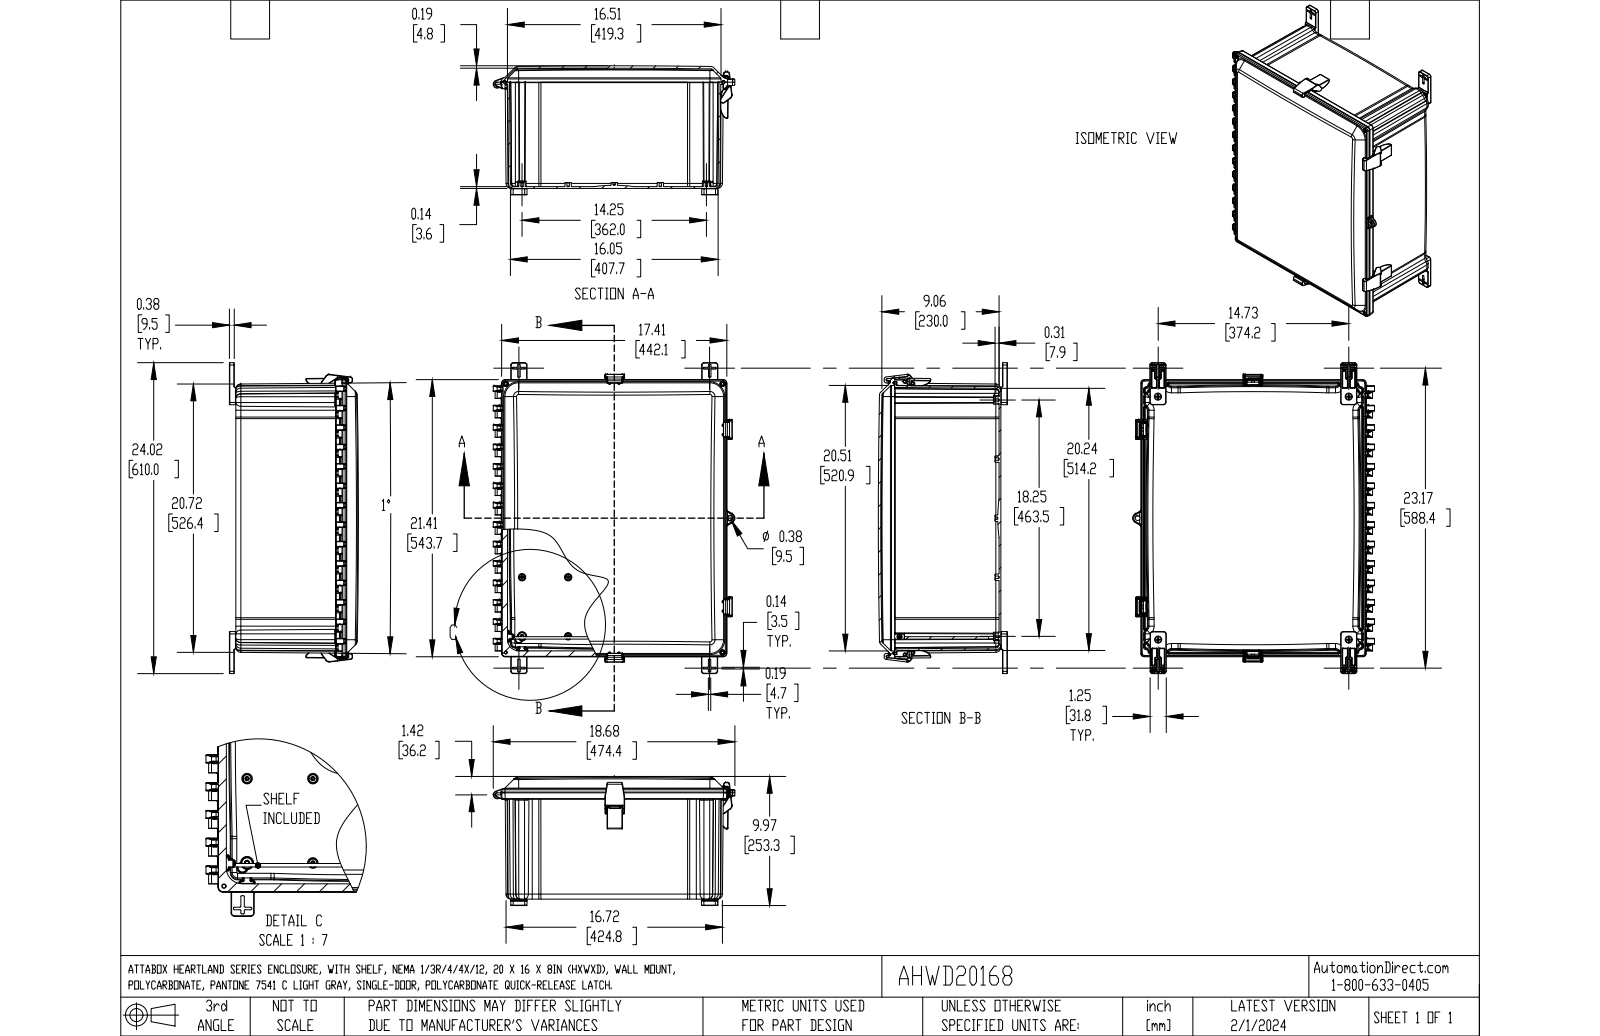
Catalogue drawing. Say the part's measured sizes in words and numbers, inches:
The part is named "AHWD20168_REV1". Its 3-D file was written by "SolidWorks 2023 (AUTOMOTIVE_DESIGN)". It is 9 solids with 2509 faces: 1002 planar, 783 cylindrical and 724 other. Overall it measures 24.017 by 18.676 by 9.973 inches. Its volume is 6 122 cubic inches and its surface area 3 211 square inches. Round holes: 25 of diameter 0.638, 4 of diameter 0.195, 4 of diameter 0.313, 4 of diameter 0.552, 3 of diameter 0.265, 2 of diameter 0.375, 1 of diameter 0.327, 1 of diameter 0.333, 1 of diameter 0.45. Round bosses or shafts: 29 of diameter 0.25, 2 of diameter 0.373, 2 of diameter 0.19, 1 of diameter 0.313. Partial cylindrical surfaces (rounded edges, fillets, slot ends): 151 of radius 0.035, 77 of radius 0.03, 68 of radius 0.065, 52 of radius 0.05, 25 of radius 0.02, 16 of radius 0.18, 14 of radius 0.03, 12 of radius 0.1. The main face-to-face distances are 0.132, 9.28, 9.148, 0.156, 15.964, 16.12, 16.273, 16.117, 0.153, 19.964. The hole center spacings are 5.657, 8.252, 9.587, 3.469, 4.469, 11.315, 11.326, 13.848.
